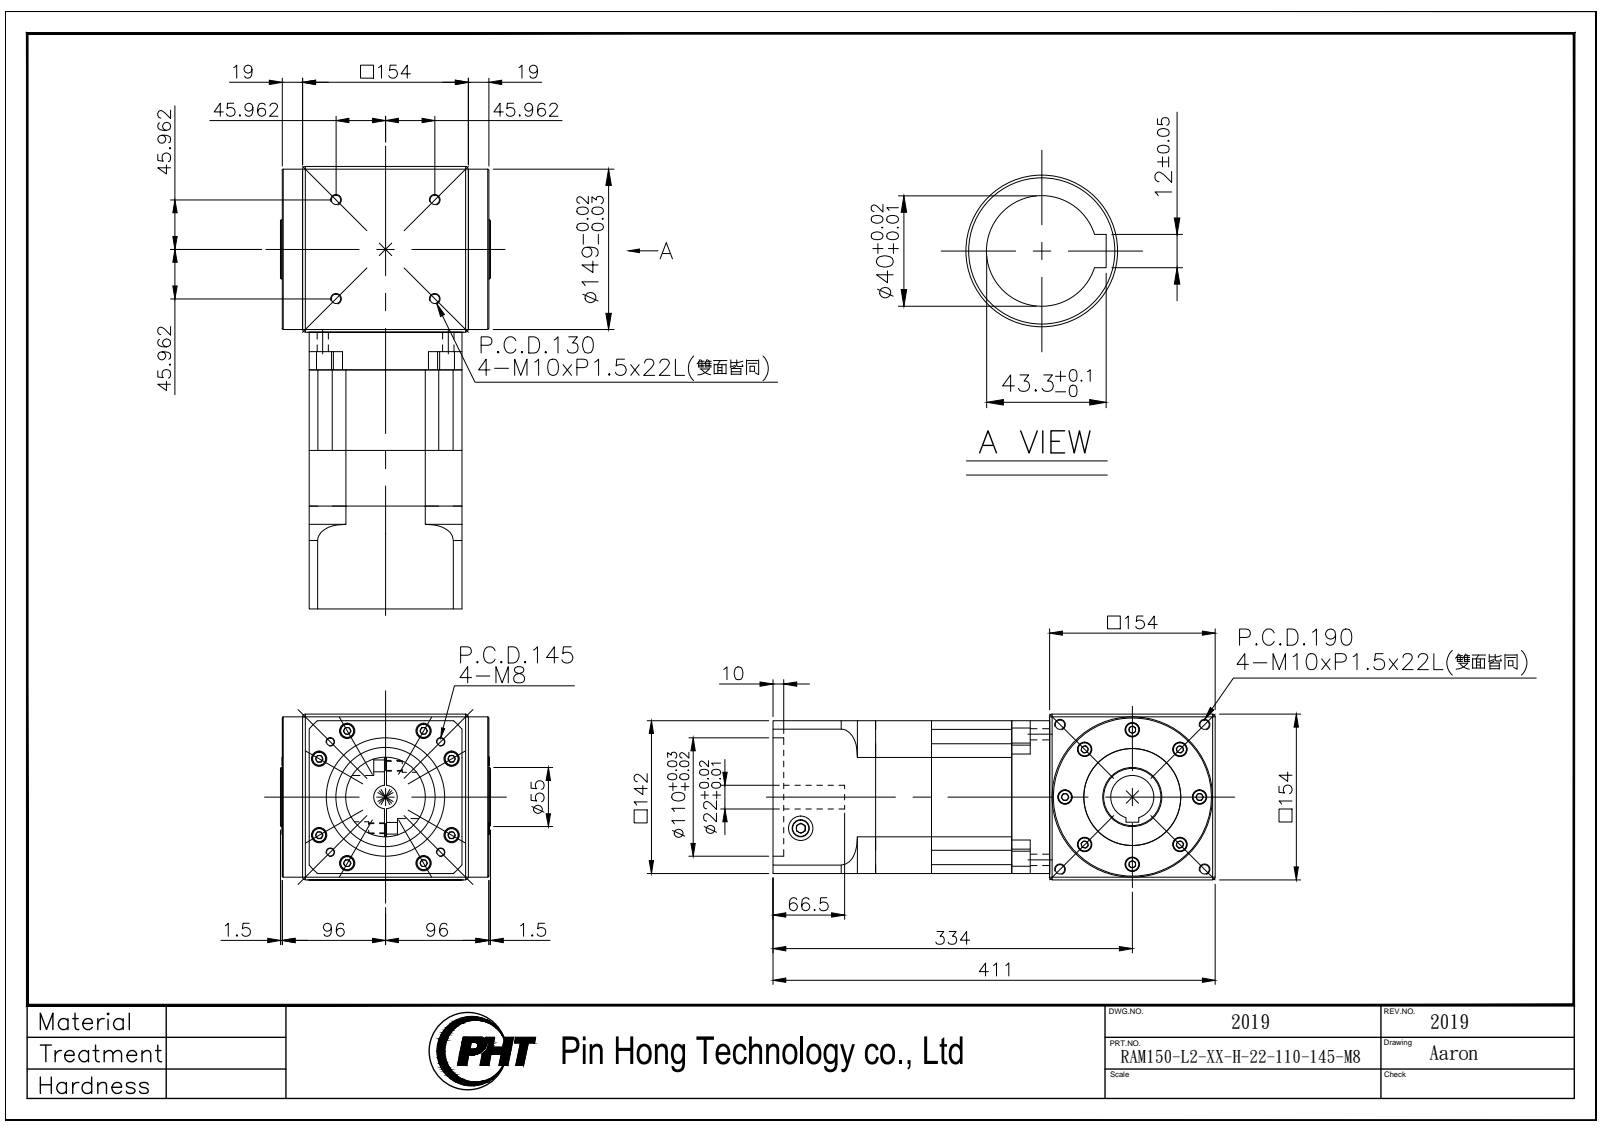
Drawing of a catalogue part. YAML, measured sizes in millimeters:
part_name: "RAM150-L2-XX-H-22-110-145-M8_2019"
step_written_by: "SolidWorks 2016 (AUTOMOTIVE_DESIGN)"
units: millimeters
bodies: {solids: 5, faces: 874, planar: 434, cylindrical: 292, other: 148}
overall_size: [411, 195, 154]
volume: 8520000
surface_area: 592364
round_holes:
  - {diameter: 8.5, count: 12}
  - {diameter: 9, count: 8}
  - {diameter: 11, count: 8}
  - {diameter: 14, count: 8}
  - {diameter: 17.5, count: 8}
  - {diameter: 6.8, count: 4}
  - {diameter: 10.5, count: 4}
  - {diameter: 22.5, count: 2}
  - {diameter: 22, count: 1}
  - {diameter: 40, count: 1}
  - {diameter: 40.6, count: 1}
  - {diameter: 92, count: 1}
round_bosses_or_shafts:
  - {diameter: 16, count: 12}
  - {diameter: 13, count: 8}
  - {diameter: 149, count: 1}
  - {diameter: 130, count: 1}
  - {diameter: 90, count: 1}
  - {diameter: 74, count: 1}
  - {diameter: 55, count: 1}
partial_cylinders:
  - {radius: 10, count: 4}
  - {radius: 80, count: 1}
  - {radius: 95, count: 1}
  - {radius: 107.4, count: 1}
face_to_face_distances: [6, 148, 154, 142, 51.8, 126.5, 74.7, 35, 161.5, 109.7]
hole_center_spacings: [71, 18.72, 18.79, 23.06, 47.83, 67.34, 82.93, 87.37]
